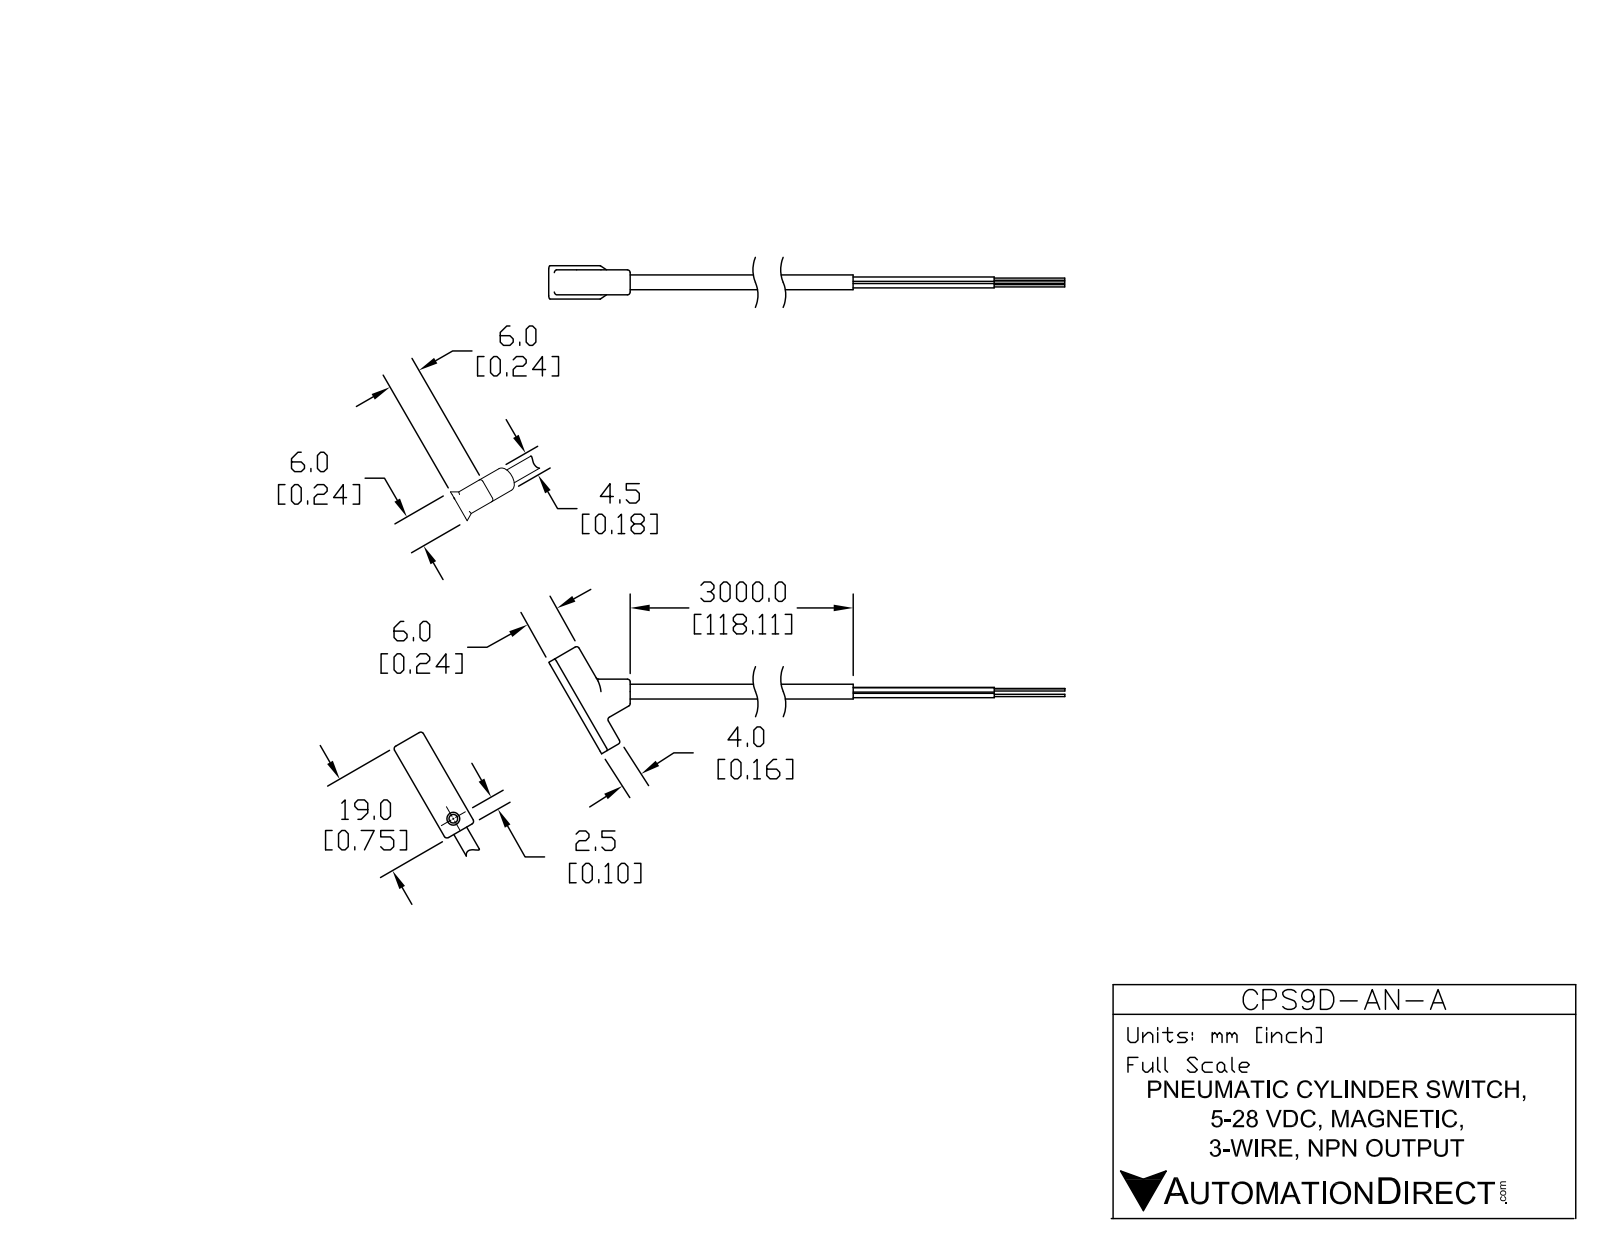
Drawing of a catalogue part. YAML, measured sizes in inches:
part_name: "CPS9D-AN-A"
step_written_by: "SolidWorks 2014 (AUTOMOTIVE_DESIGN)"
units: inches
bodies: {solids: 1, faces: 83, planar: 24, cylindrical: 39, other: 20}
overall_size: [5.535, 3.459, 0.236]
volume: 0.076
surface_area: 2.64
round_holes:
  - {diameter: 0.091, count: 1}
round_bosses_or_shafts:
  - {diameter: 0.031, count: 3}
  - {diameter: 0.016, count: 3}
  - {diameter: 0.105, count: 1}
partial_cylinders:
  - {radius: 0.02, count: 20}
  - {radius: 0.089, count: 1}
face_to_face_distances: [0.177, 0.236, 0.551, 0.748, 0.197, 0.157, 0.079, 4.421, 0.157, 0.236]
